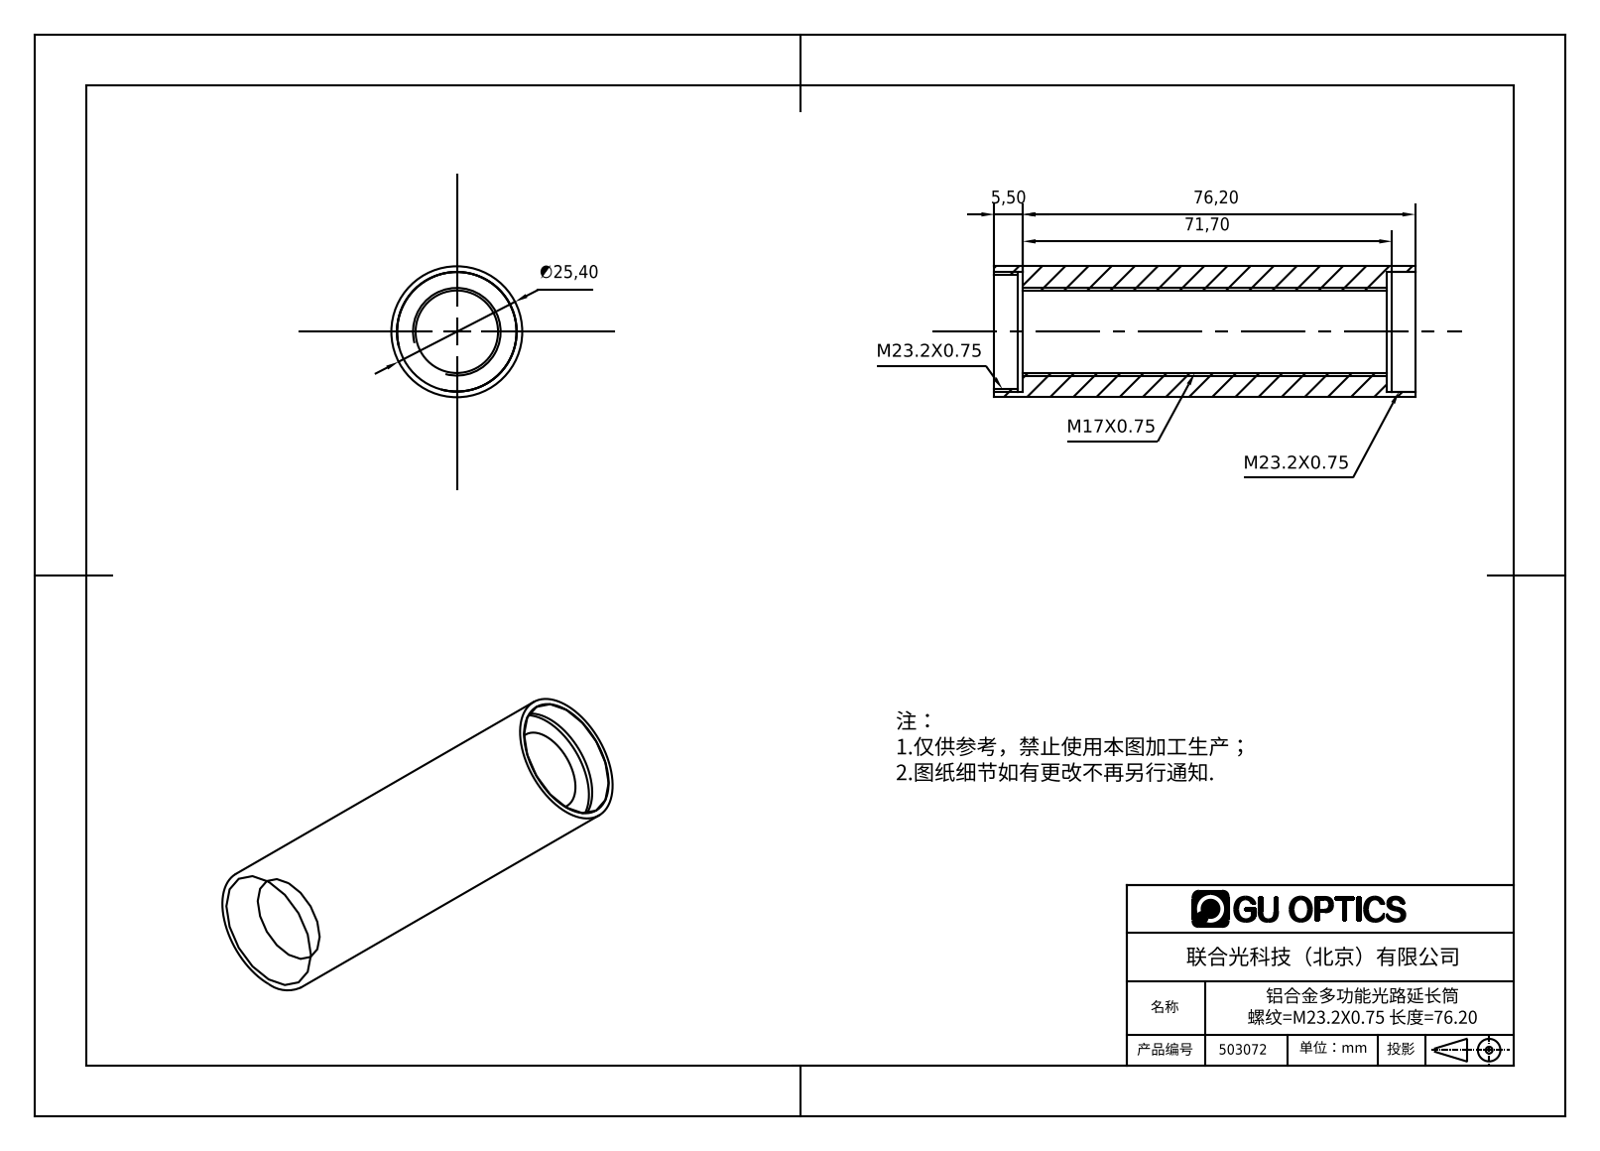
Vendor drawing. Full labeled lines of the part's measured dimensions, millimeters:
Part name (STEP PRODUCT): 503072
STEP written by: SolidWorks 2016 (AUTOMOTIVE_DESIGN)
Units: millimetres
Bodies: 1 solid, 18 faces (6 planar, 12 cylindrical, 0 other)
Overall size (bounding box): 81.7 × 25.4 × 25.4
Volume: 22 679 mm³ · Surface area: 11 574 mm²
Round holes (diameter × count): ⌀16 ×1, ⌀22.2 ×1, ⌀23.2 ×1, ⌀23.4 ×1
Round bosses / shafts (diameter × count): ⌀25.4 ×1
Main face-to-face distances: 70.7, 5.5, 76.2, 81.7, 4.5, 77.2, 1, 71.7, 72.7
